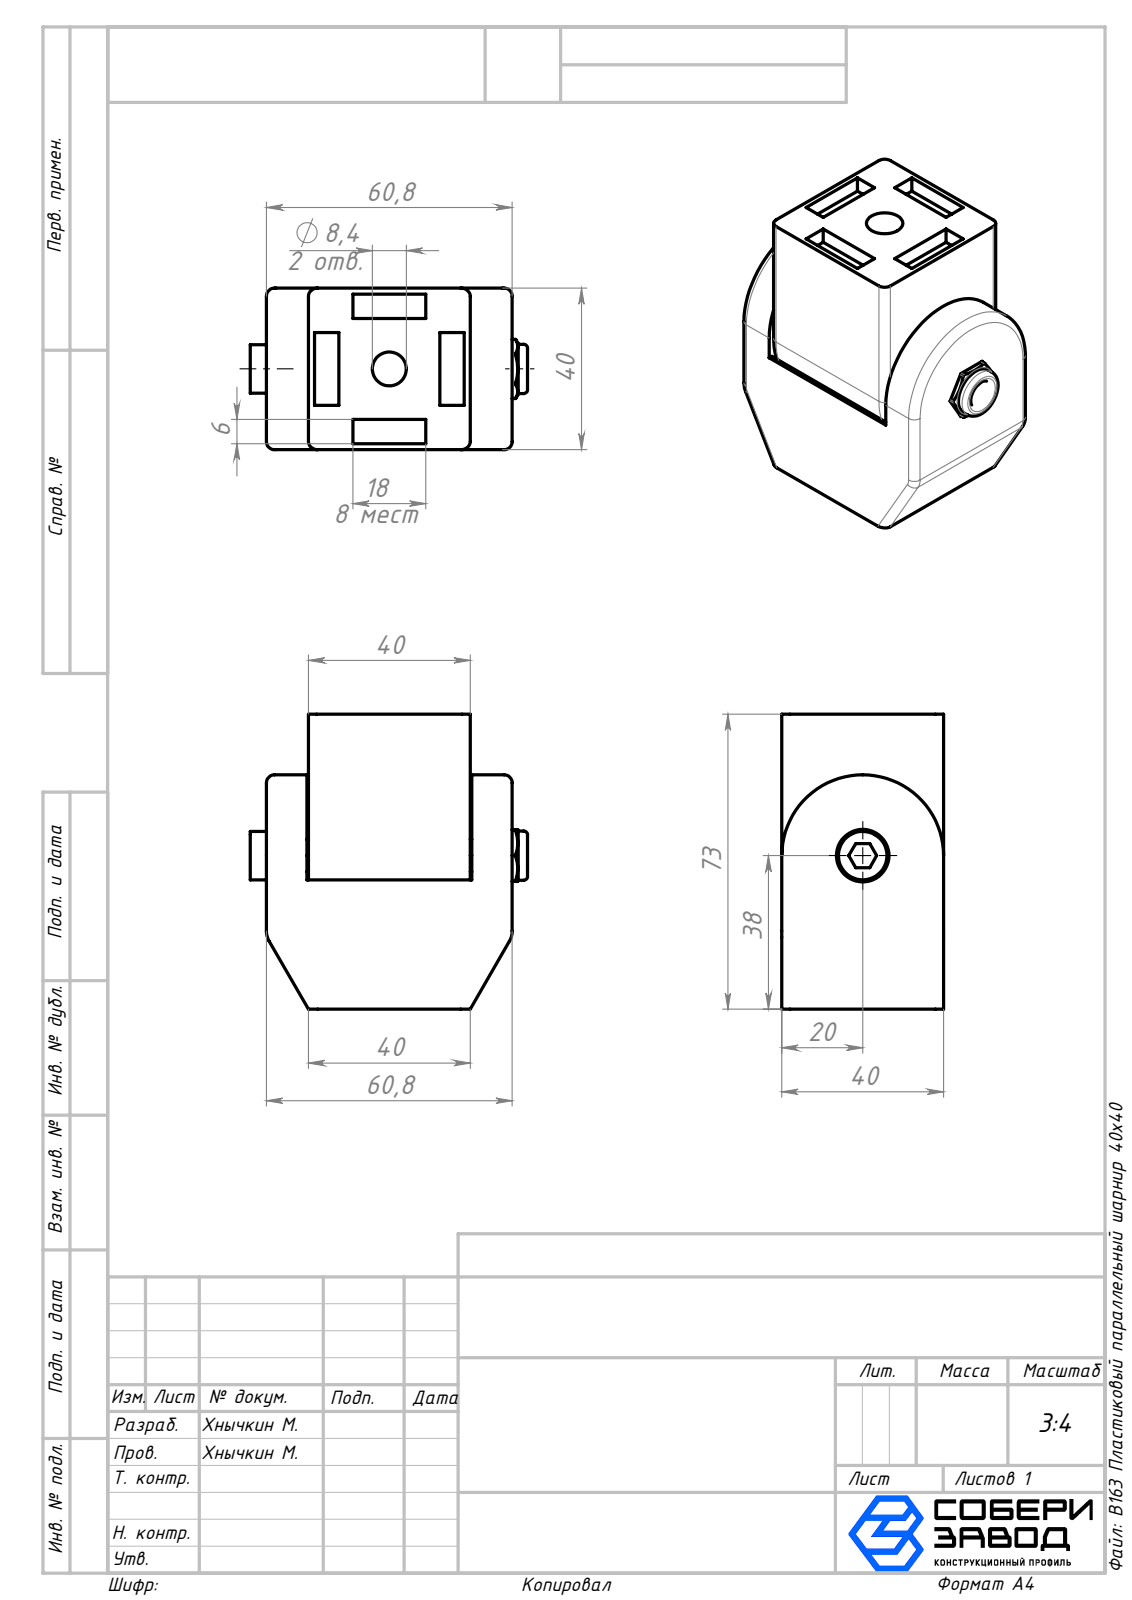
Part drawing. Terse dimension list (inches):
name: B163 Пластиковый параллельный шарнир 40х40; B163 Часть_2_00; B163 Винт Din 912 М8_00; B163 Самоконтрящаяся гайка М8_00 (+2 more)
written by: SolidWorks 2026 (AUTOMOTIVE_DESIGN)
unit: in
bodies: 5 solids, 171 faces (97 planar, 53 cylindrical, 21 other)
size: 2.874 × 2.7 × 1.575
volume: 8.788 in³; area: 61.01 in²
holes: 2× ⌀0.331, 1× ⌀0.276, 1× ⌀0.283, 1× ⌀0.315, 1× ⌀0.354, 1× ⌀0.512, 1× ⌀0.945
bosses: 1× ⌀1.575, 1× ⌀0.48, 1× ⌀0.472
rounds: 12× R0.079, 6× R0.02, 2× R0.197
face distances: 1.575, 0.015, 1.59, 0.394, 0.409, 1.984, 1.999, 0.157, 1.606, 2.393
